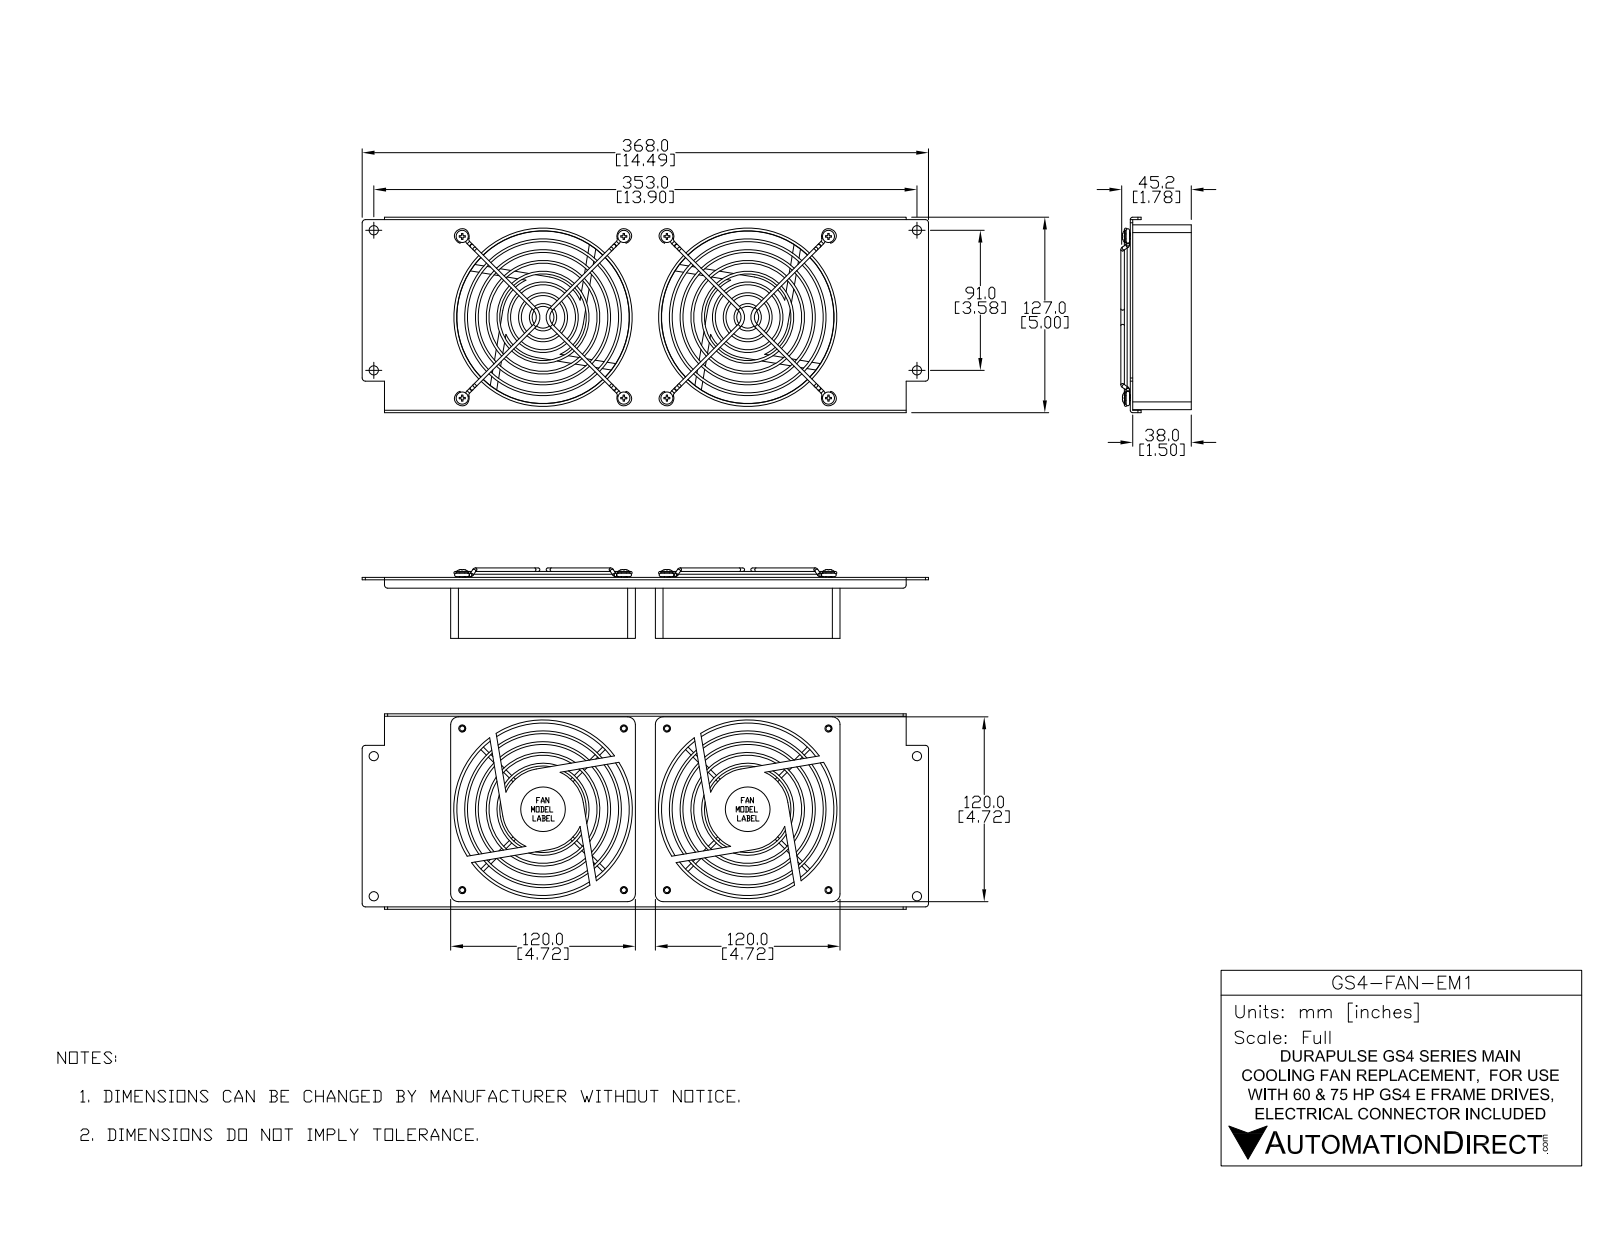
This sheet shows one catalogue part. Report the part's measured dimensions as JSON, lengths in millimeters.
{"part_name": "GS4-FAN-EM1", "step_written_by": "SolidWorks 2015 (AUTOMOTIVE_DESIGN)", "units": "millimeters", "bodies": {"solids": 0, "faces": 175, "planar": 48, "cylindrical": 52, "other": 75}, "overall_size": [368, 127, 45.75], "round_holes": [[116, 1]], "round_bosses_or_shafts": [[6, 4], [116, 1]], "partial_cylinders_radius": [[1.15, 8], [5, 8], [2, 6], [1.6, 2], [26.5, 2]], "face_to_face_distances": [1.6, 120, 38, 39.6, 48.41, 4.61, 133, 43.8, 131.14, 21.94]}
